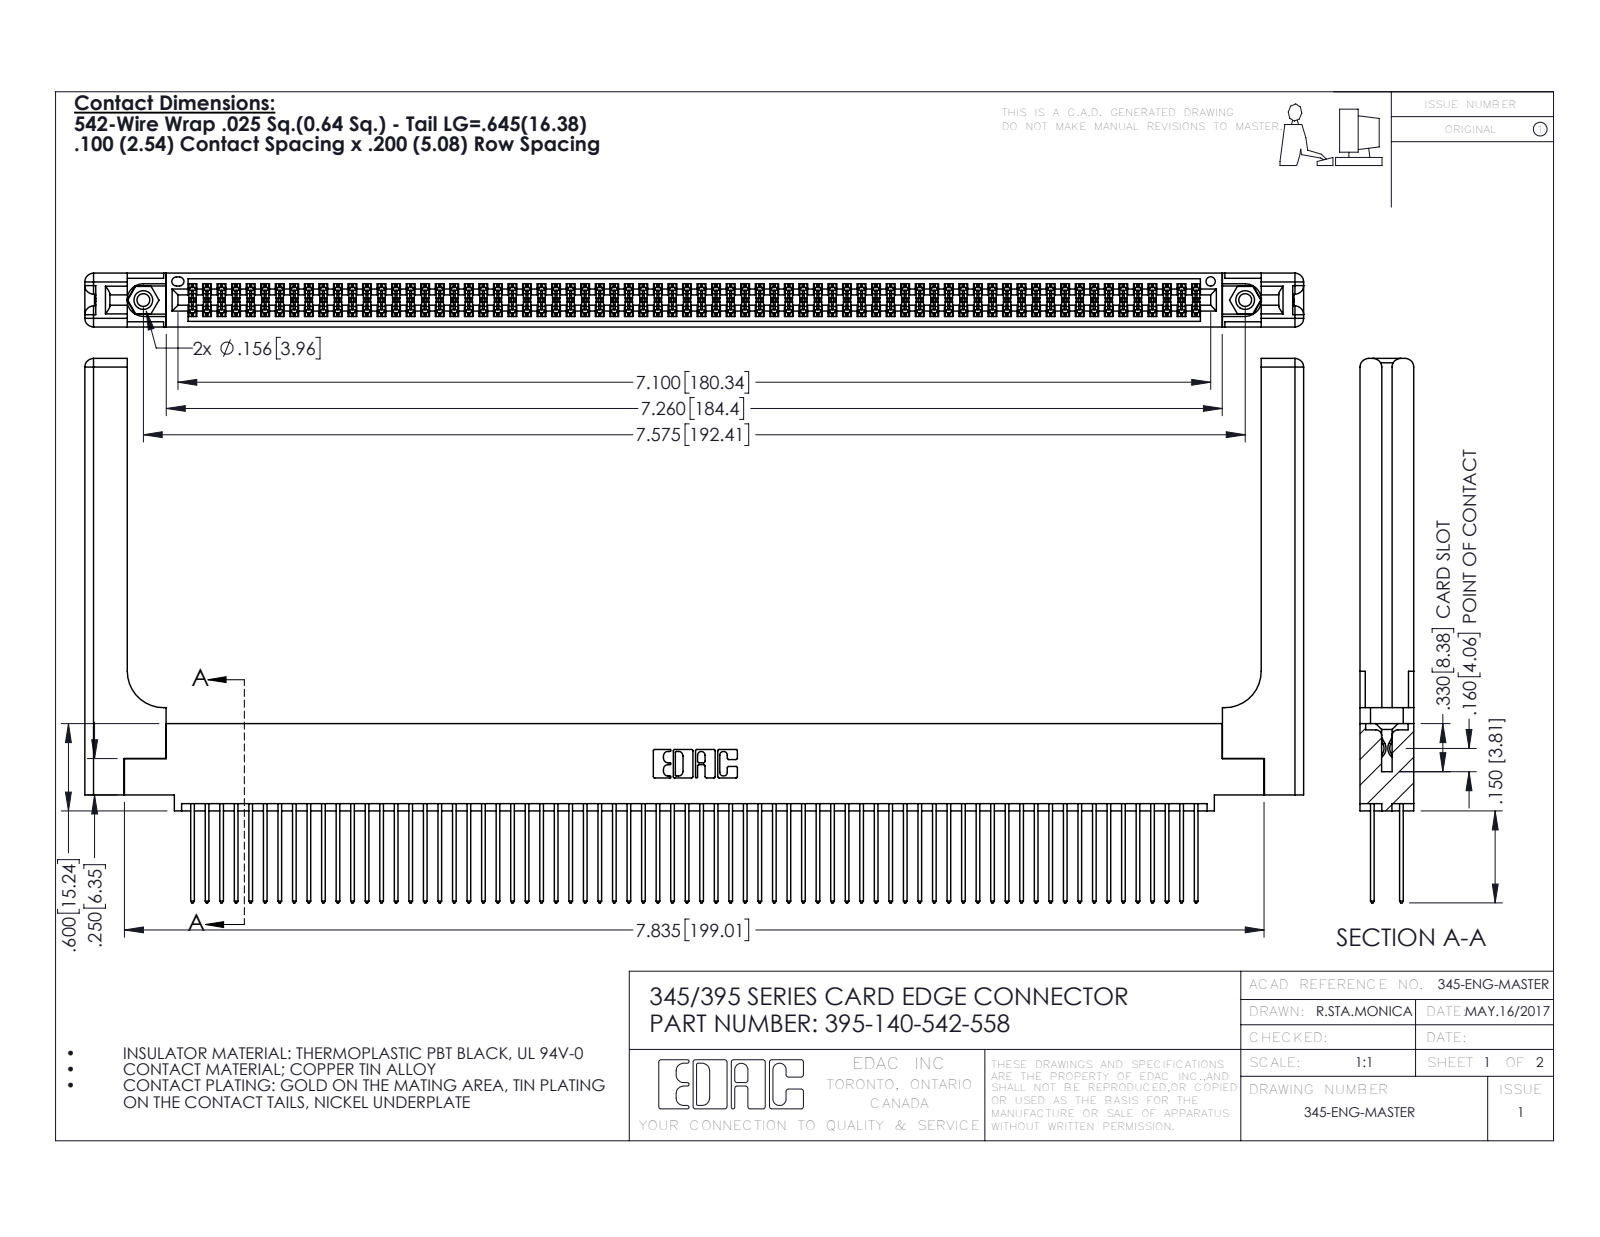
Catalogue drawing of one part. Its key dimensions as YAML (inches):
part_name: "395-140-542-558; 345-292-001_345-293-142; 345-220-058_345-220-058; 345-250-001_345-250-001-102 (+1 more)"
step_written_by: "SolidWorks 2016 (CONFIG_CONTROL_DESIGN)"
units: inches
bodies: {solids: 145, faces: 7386, planar: 4852, cylindrical: 2474, other: 60}
overall_size: [8.379, 3.742, 0.37]
volume: 1.83
surface_area: 62.84
round_holes:
  - {diameter: 0.089, count: 2}
  - {diameter: 0.125, count: 2}
  - {diameter: 0.156, count: 2}
  - {diameter: 0.064, count: 1}
round_bosses_or_shafts:
  - {diameter: 0.155, count: 2}
partial_cylinders:
  - {radius: 0.006, count: 210}
  - {radius: 0.01, count: 140}
  - {radius: 0.01, count: 22}
  - {radius: 0.06, count: 16}
  - {radius: 0.007, count: 6}
  - {radius: 0.031, count: 6}
  - {radius: 0.026, count: 3}
  - {radius: 0.014, count: 2}
face_to_face_distances: [0.072, 0.298, 0.098, 0.272, 0.025, 0.2, 0.37, 0.225, 0.175, 0.148]
hole_center_spacings: [0.27, 7.339, 7.575]
